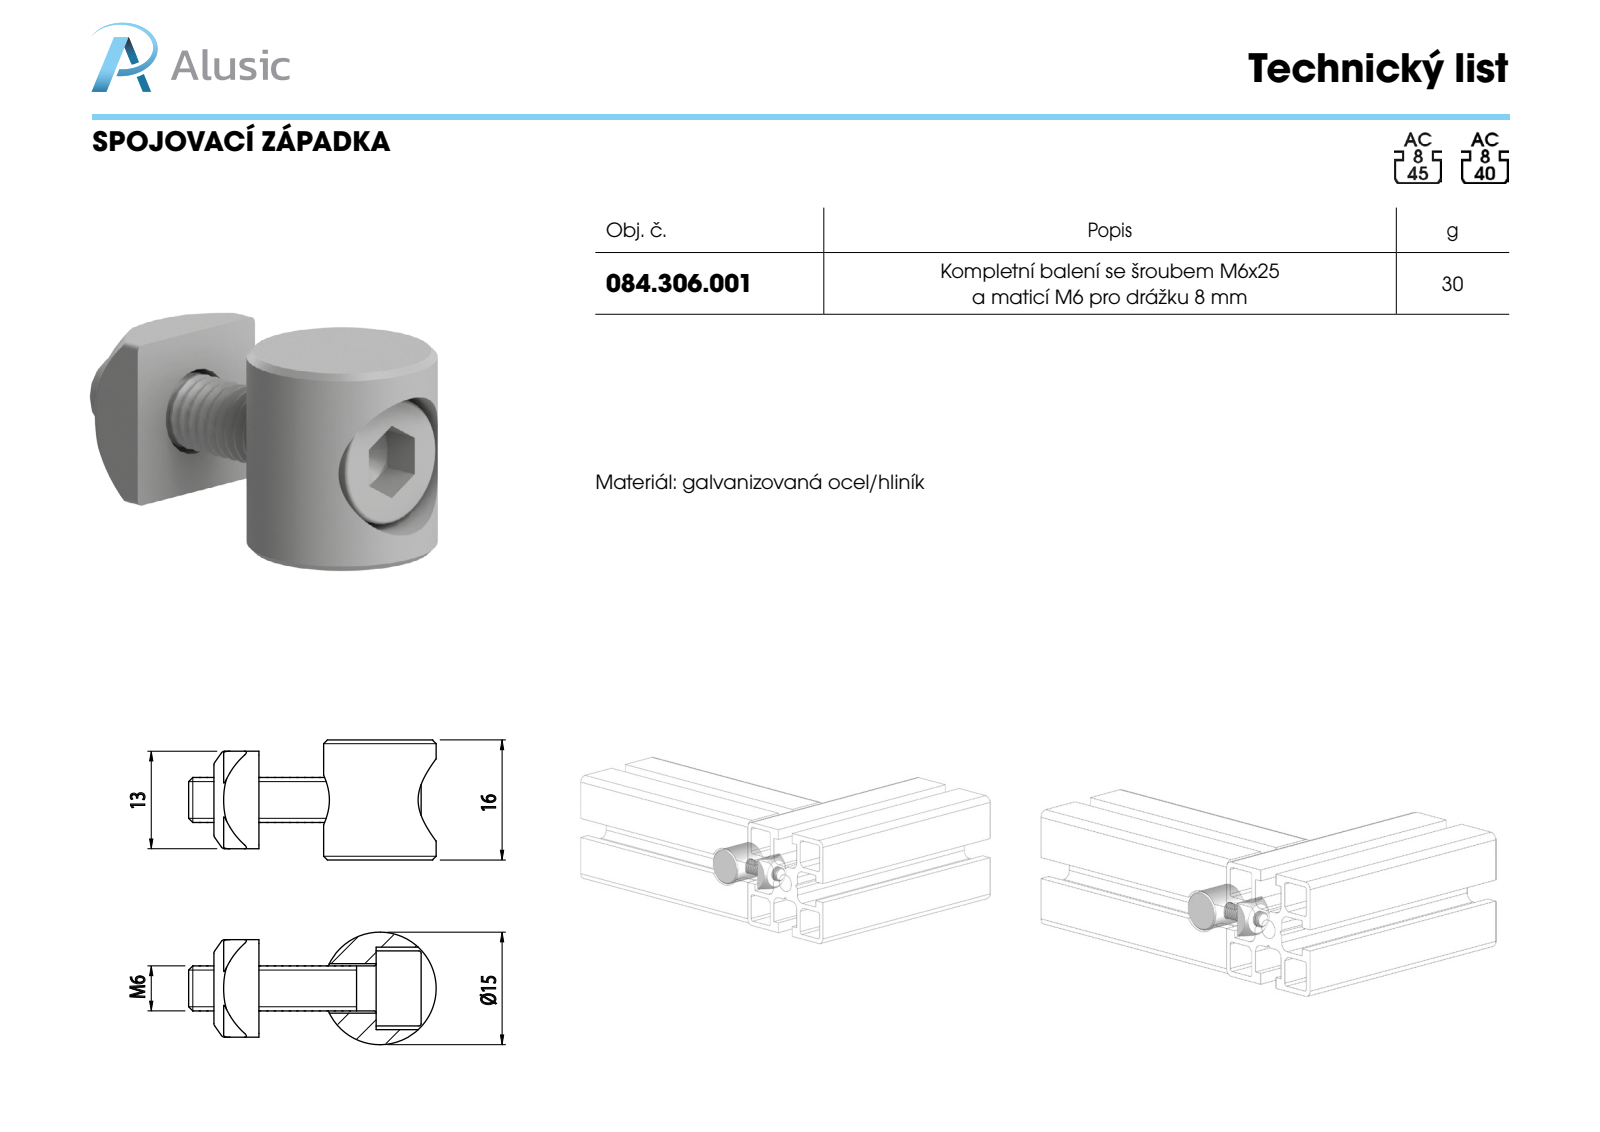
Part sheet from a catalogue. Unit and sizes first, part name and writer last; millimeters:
Units: millimetres
Overall size (bounding box): 16 × 15 × 15
Round holes (diameter × count): ⌀6.6 ×1, ⌀11 ×1
Round bosses / shafts (diameter × count): ⌀15 ×1
Main face-to-face distances: 16
Volume: 1 874 mm³ · Surface area: 1 376 mm²
Bodies: 1 solid, 13 faces (3 planar, 6 cylindrical, 4 other)
Part name (STEP PRODUCT): 084.306.001
STEP written by: SolidWorks 2011 (CONFIG_CONTROL_DESIGN)
